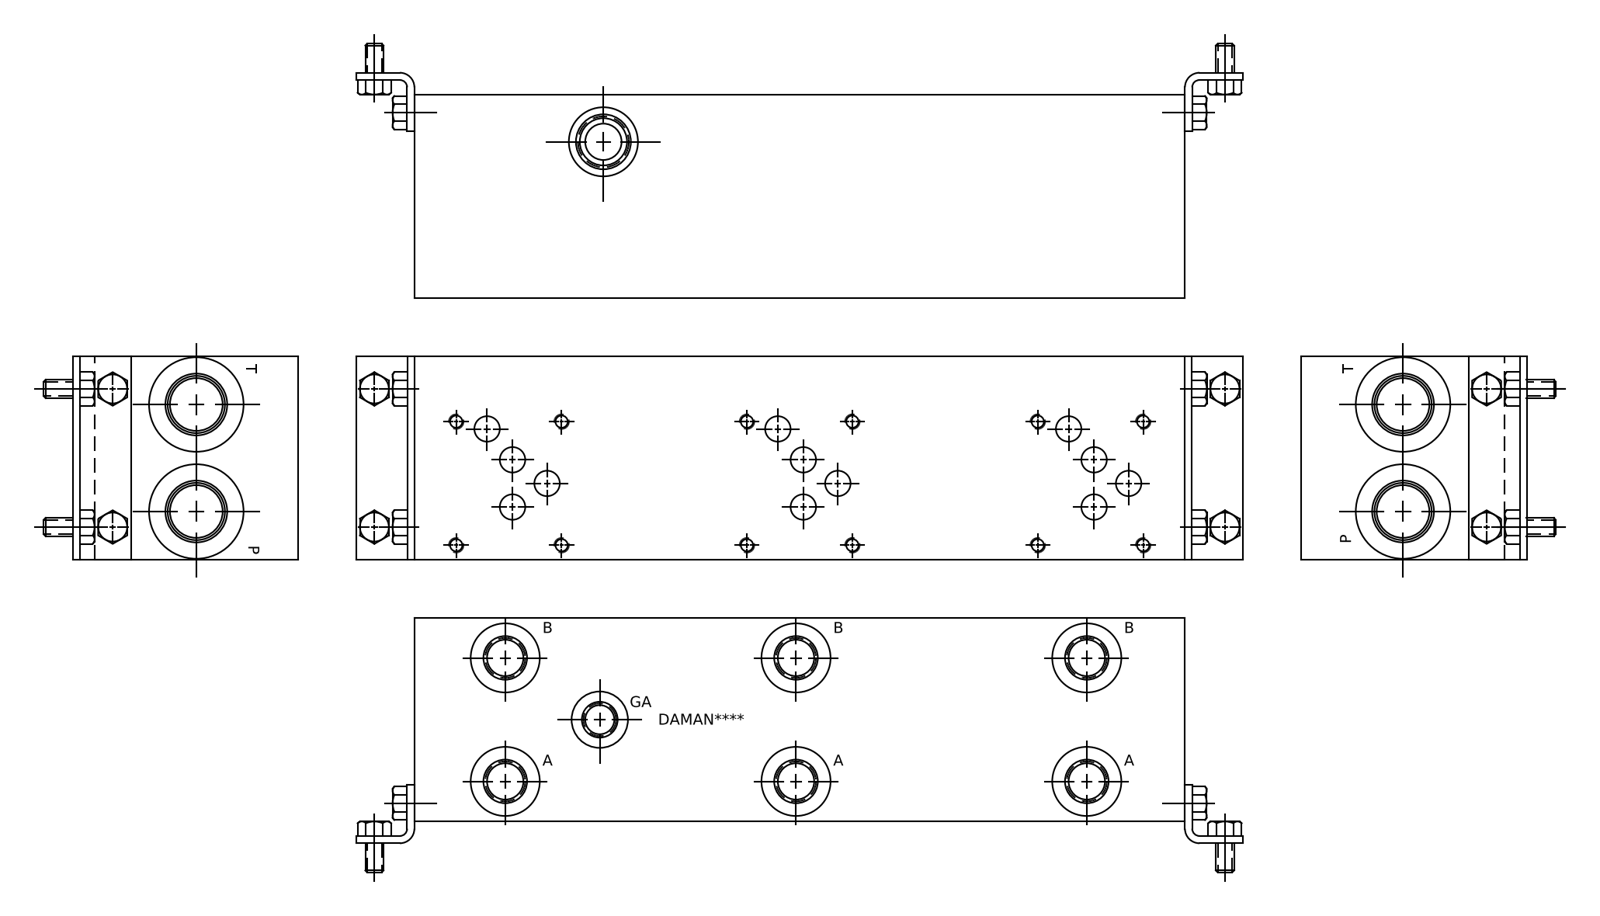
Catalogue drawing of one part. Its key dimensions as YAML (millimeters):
part_name: "Part_AD05P035S~C_3D"
step_written_by: "Autodesk Inventor 2020 (AUTOMOTIVE_DESIGN)"
units: millimeters
bodies: {solids: 1, faces: 778, planar: 399, cylindrical: 105, other: 274}
overall_size: [336.55, 88.9, 88.9]
volume: 2515000
surface_area: 165205
round_holes:
  - {diameter: 5.11, count: 12}
  - {diameter: 6.35, count: 12}
  - {diameter: 11.13, count: 12}
  - {diameter: 15.88, count: 6}
  - {diameter: 17.5, count: 6}
  - {diameter: 19.05, count: 6}
  - {diameter: 19.25, count: 6}
  - {diameter: 30.63, count: 6}
  - {diameter: 6.53, count: 2}
  - {diameter: 7.92, count: 2}
  - {diameter: 23.01, count: 2}
  - {diameter: 24.92, count: 2}
face_to_face_distances: [88.9, 0.79, 336.55, 88.11, 335.76, 334.97, 19.05, 19.84, 316.71, 315.92]
hole_center_spacings: [127, 254, 138, 46.05, 70.95, 53.98, 18.27, 29.74]
